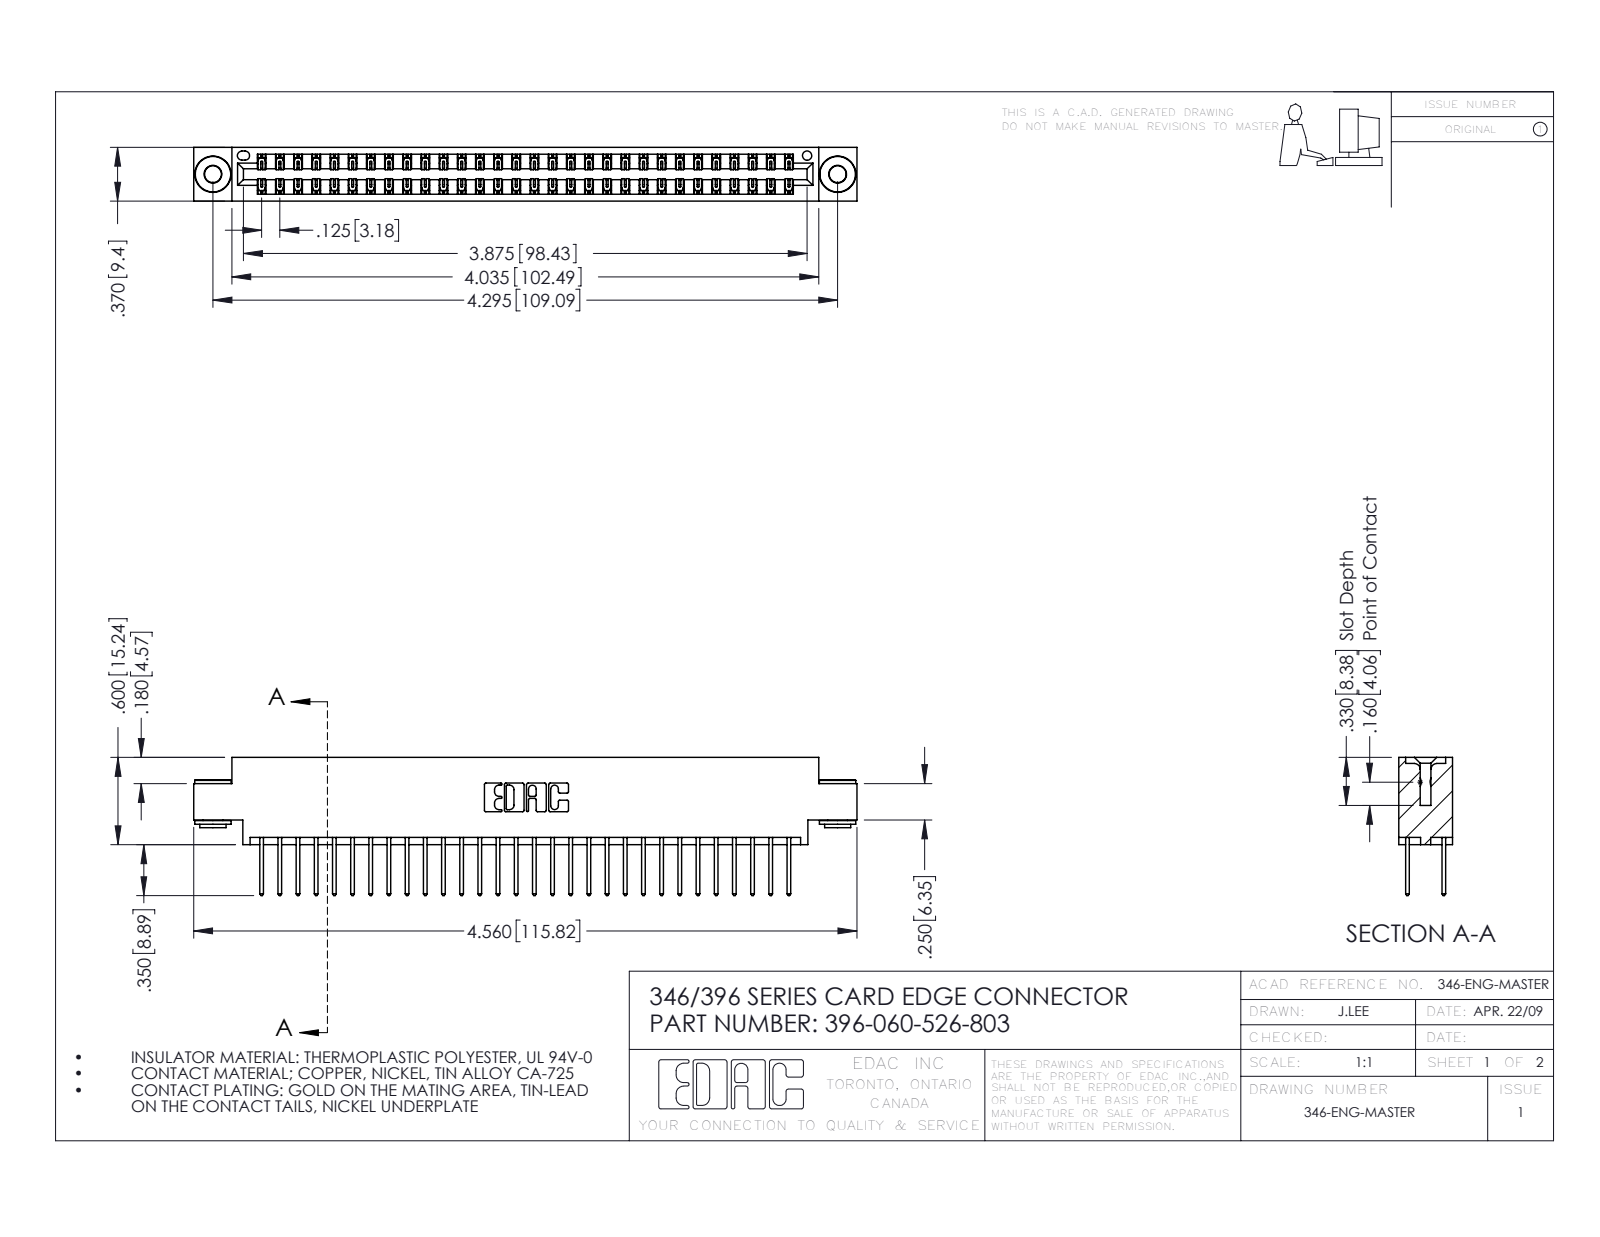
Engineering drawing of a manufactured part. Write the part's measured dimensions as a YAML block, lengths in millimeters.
part_name: "346 Part_0.170 Offset - 0.156 Dia-TH; 345-250-002_345-250-002-102; 345-292-001_345-293-126; 396-060-526-803"
step_written_by: "SolidWorks 2016 (CONFIG_CONTROL_DESIGN)"
units: millimeters
bodies: {solids: 63, faces: 3284, planar: 2190, cylindrical: 1086, other: 8}
overall_size: [115.8, 24.1, 9.4]
volume: 11200
surface_area: 15990
round_holes:
  - {diameter: 2.9, count: 2}
  - {diameter: 4, count: 2}
  - {diameter: 1.6, count: 1}
round_bosses_or_shafts:
  - {diameter: 6.4, count: 2}
  - {diameter: 4.6, count: 2}
  - {diameter: 3.5, count: 2}
partial_cylinders:
  - {radius: 0.2, count: 90}
  - {radius: 0.3, count: 60}
  - {radius: 0.3, count: 22}
  - {radius: 0.2, count: 6}
  - {radius: 0.8, count: 6}
  - {radius: 0.7, count: 3}
  - {radius: 0.4, count: 2}
  - {radius: 0.6, count: 2}
face_to_face_distances: [1.2, 8.2, 6.4, 9.4, 0.6, 1.8, 7.6, 7, 3.8, 5.6]
hole_center_spacings: [6.2, 103.8, 109.1]
